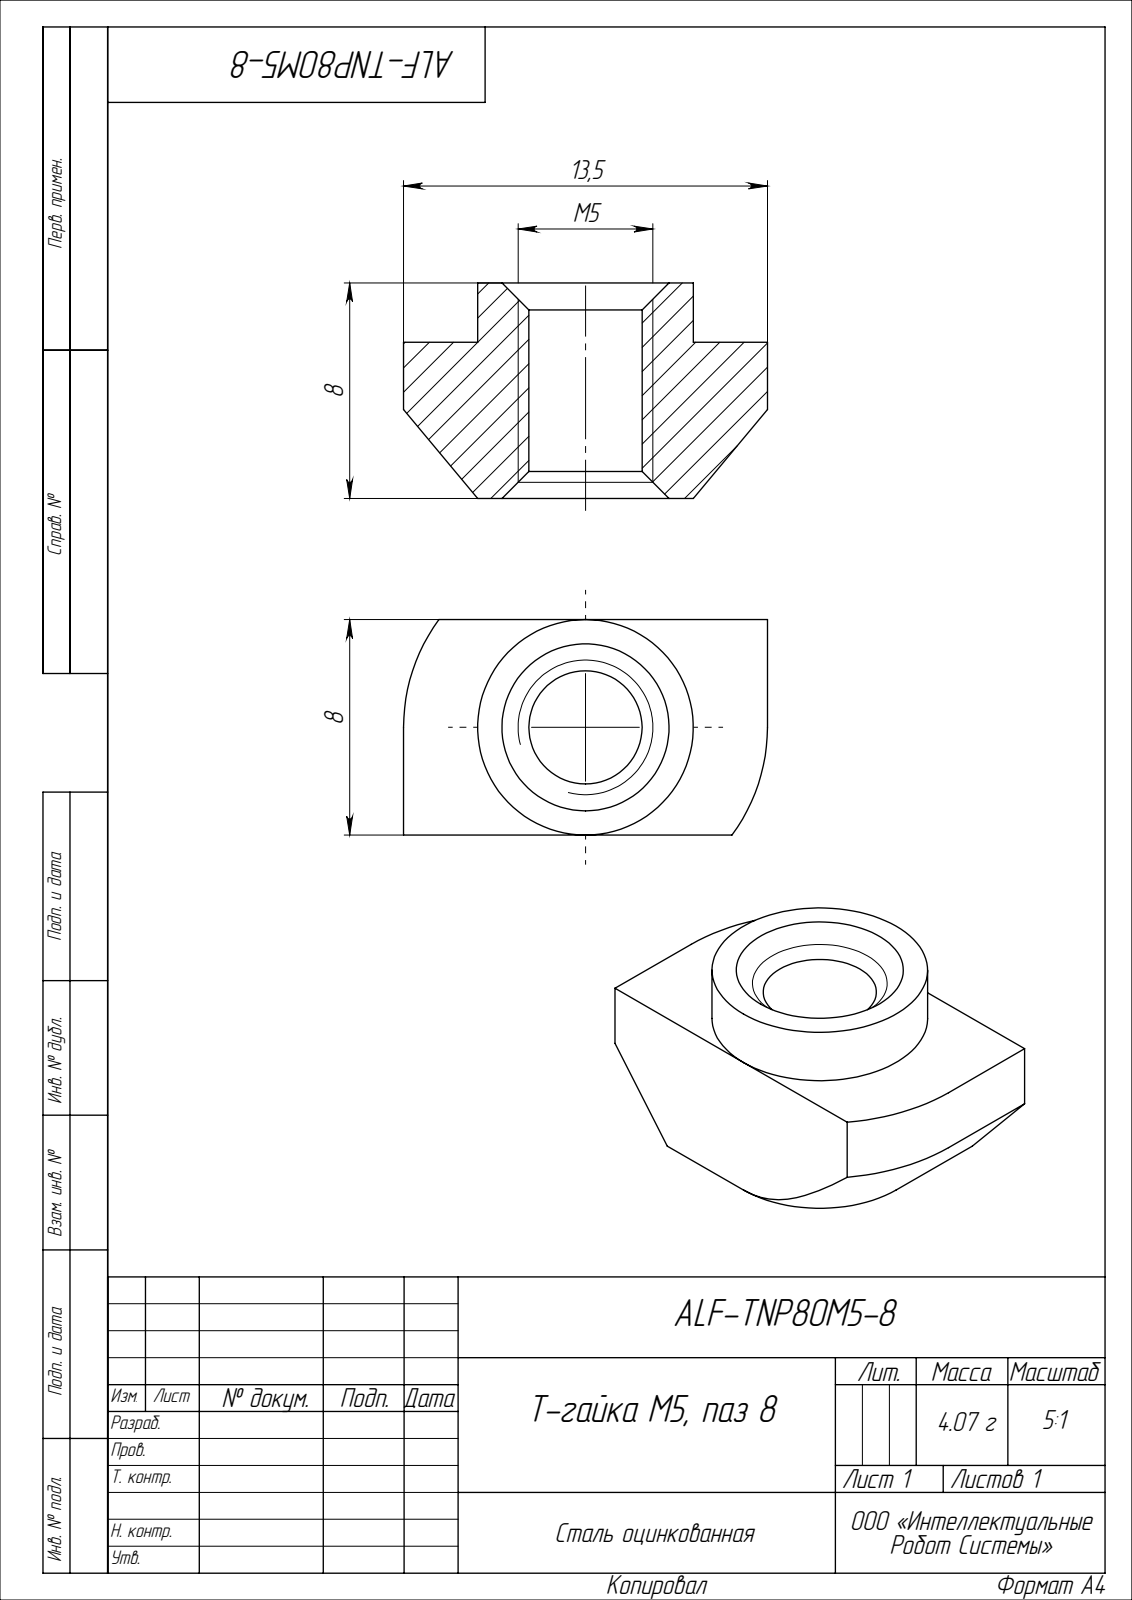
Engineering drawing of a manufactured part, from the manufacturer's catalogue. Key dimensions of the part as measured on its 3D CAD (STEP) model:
Part name (STEP PRODUCT): ALF-TNP80M5-8
STEP written by: SolidWorks 2022 (CONFIG_CONTROL_DESIGN)
Units: millimetres
Bodies: 1 solid, 22 faces (10 planar, 6 cylindrical, 6 other)
Overall size (bounding box): 13.5 × 8 × 8
Volume: 515 mm³ · Surface area: 517 mm²
Round holes (diameter × count): ⌀4.2 ×1
Round bosses / shafts (diameter × count): ⌀8 ×1
Partial cylindrical surfaces — rounded edges, fillets, slot ends (radius × count): R6.75 ×1
Main face-to-face distances: 8, 5.8, 2.2, 13.5
